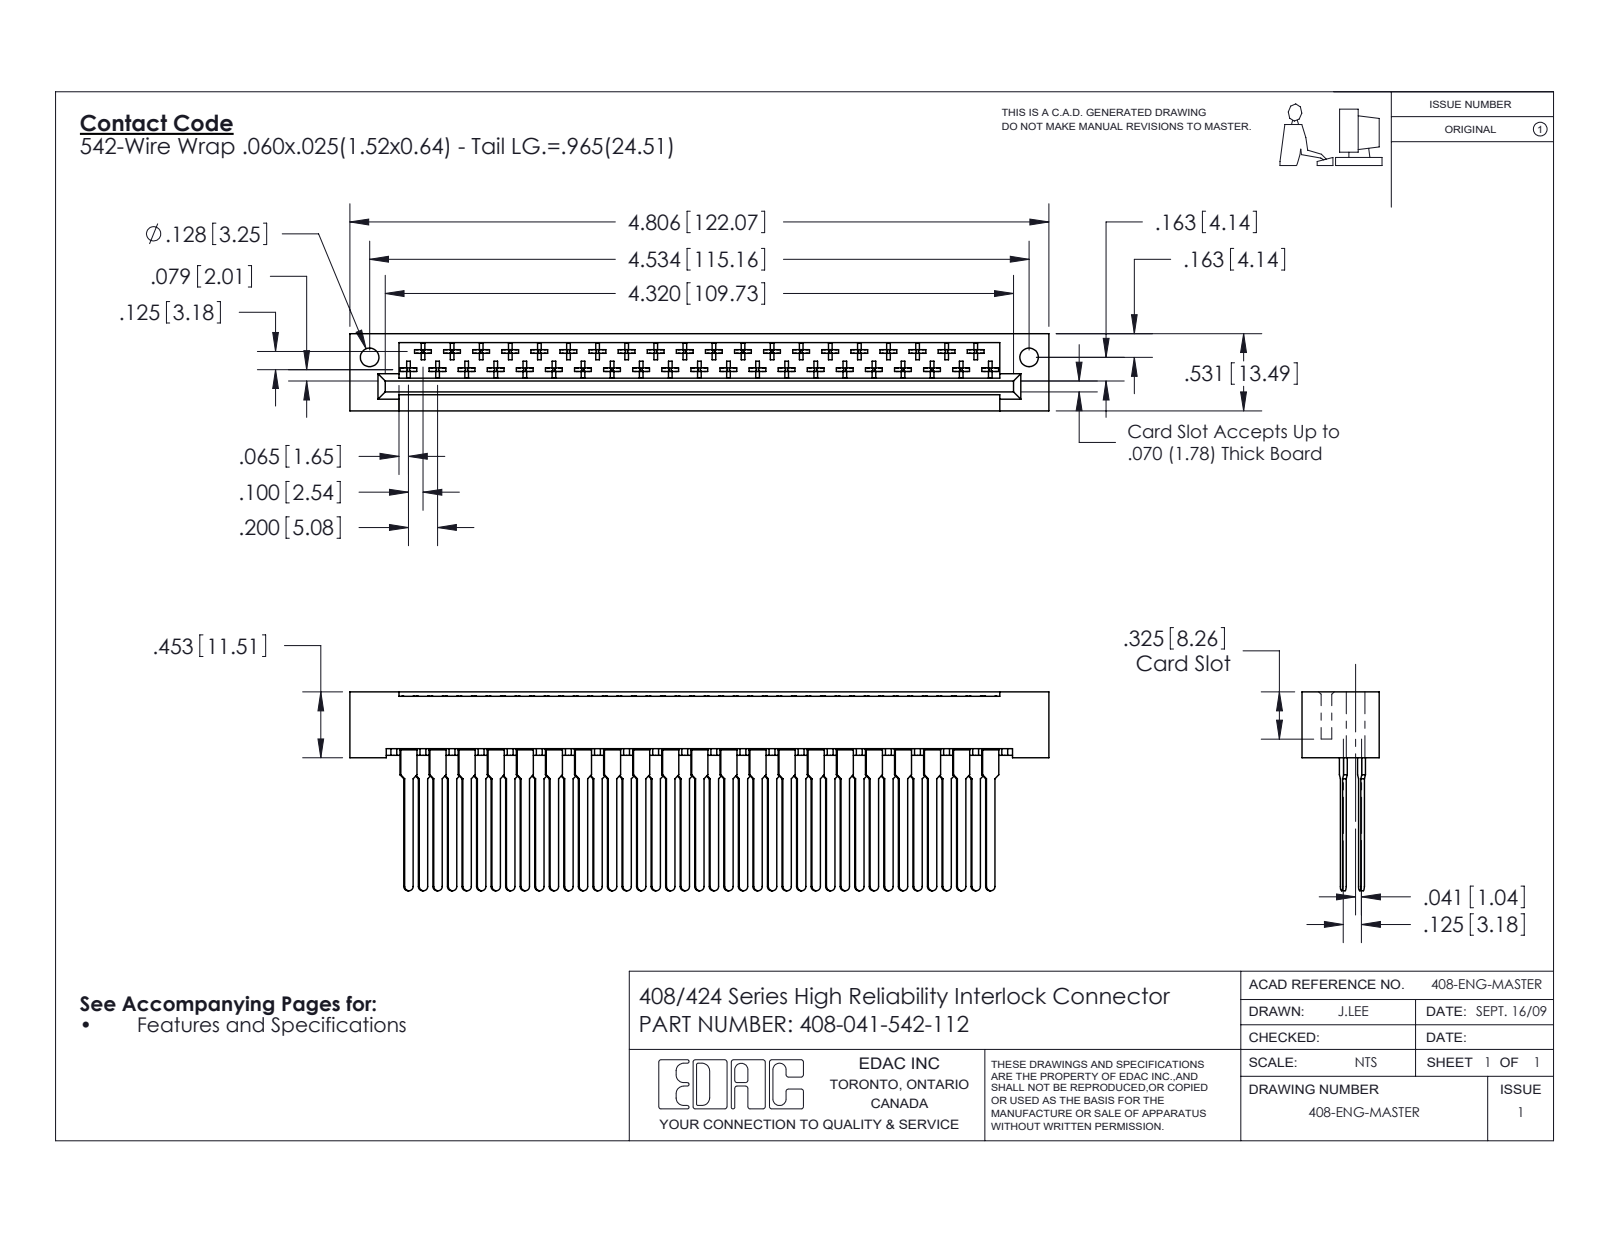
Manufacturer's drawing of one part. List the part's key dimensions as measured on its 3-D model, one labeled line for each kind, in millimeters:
Part name (STEP PRODUCT): 408-047-542-112; 408-290-001_408-290-142; 408 Part_041 - 1
STEP written by: SolidWorks 2016 (CONFIG_CONTROL_DESIGN)
Units: millimetres
Bodies: 42 solids, 2217 faces (1676 planar, 377 cylindrical, 164 other)
Overall size (bounding box): 122.1 × 34.7 × 13.5
Volume: 14 900 mm³ · Surface area: 20 530 mm²
Round holes (diameter × count): ⌀3.3 ×2
Partial cylindrical surfaces — rounded edges, fillets, slot ends (radius × count): R0.3 ×246, R0.5 ×43, R0.8 ×41
Main face-to-face distances: 13.5, 2.5, 3.2, 0.6, 0.6, 10.2, 6.6, 6.9, 6, 7.5
Hole centre spacings: 115.2
